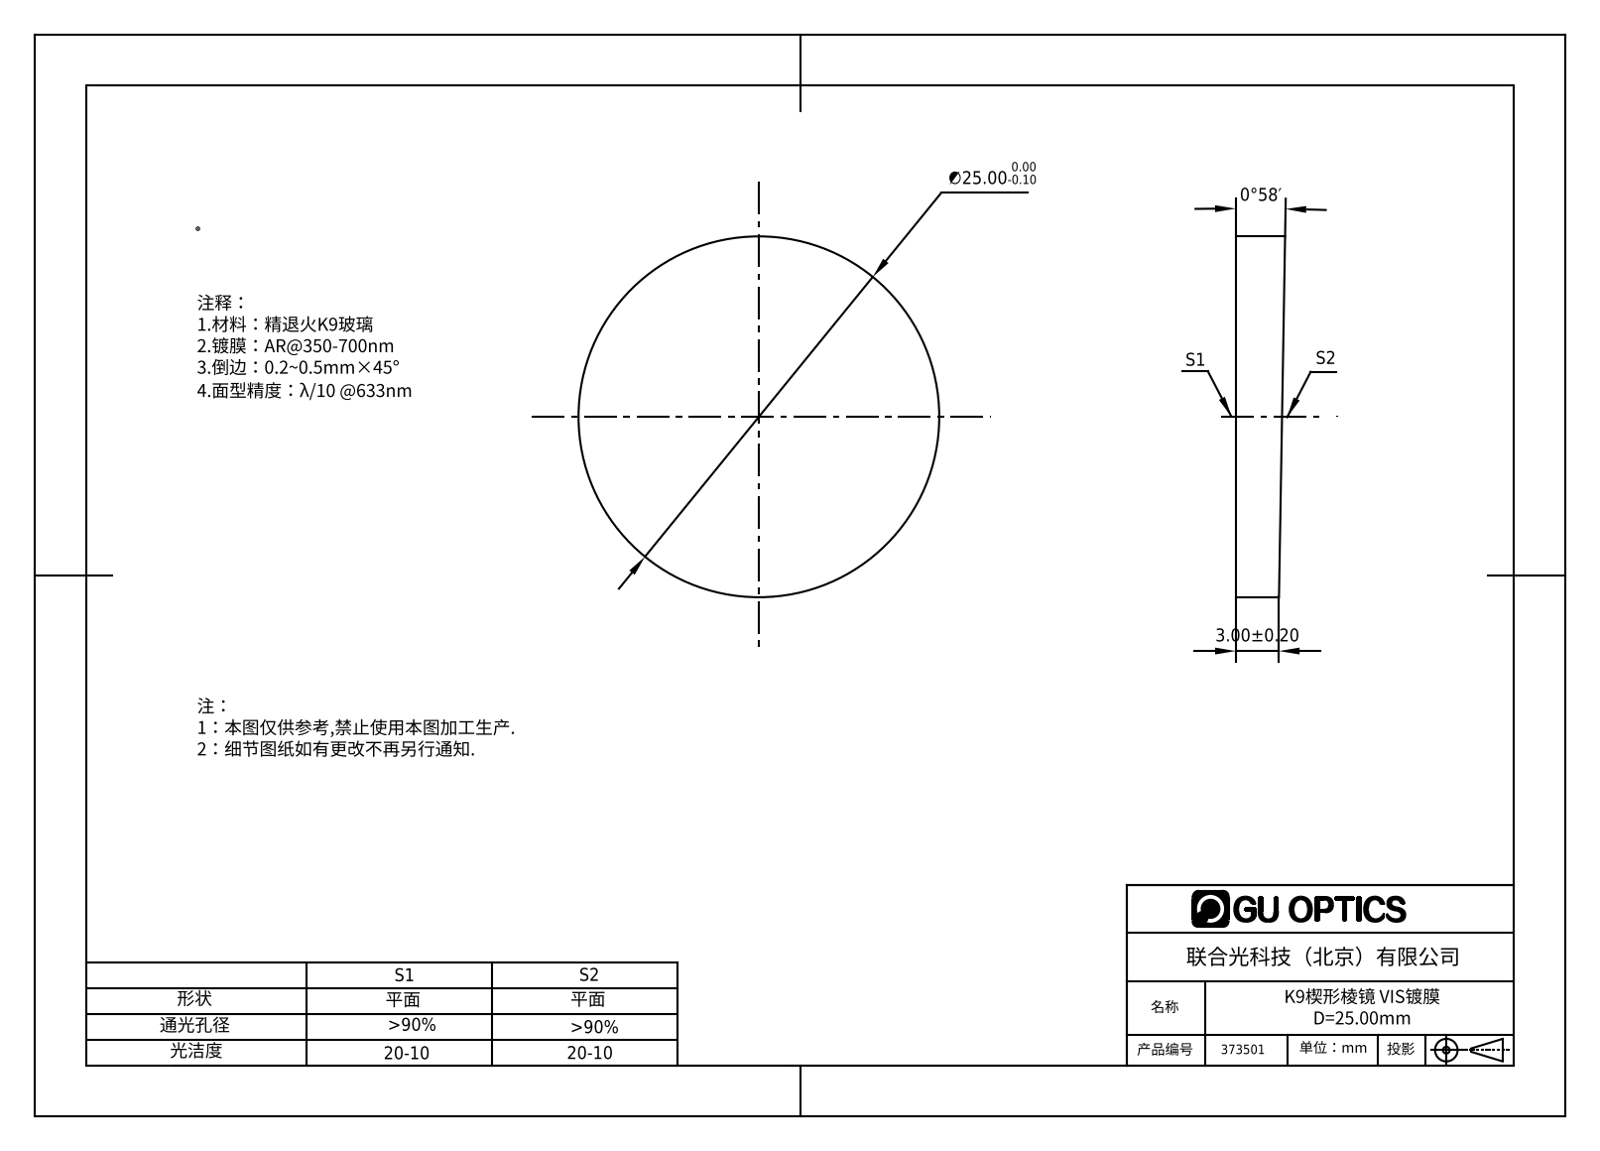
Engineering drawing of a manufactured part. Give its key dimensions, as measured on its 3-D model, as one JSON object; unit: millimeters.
{"part_name": "373500", "step_written_by": "SolidWorks 2016 (CONFIG_CONTROL_DESIGN)", "units": "millimeters", "bodies": {"solids": 1, "faces": 4, "planar": 2, "cylindrical": 2, "other": 0}, "overall_size": [25, 25, 3.55], "volume_mm3": 1640, "surface_area_mm2": 1244, "round_bosses_or_shafts": [[25, 1]]}
